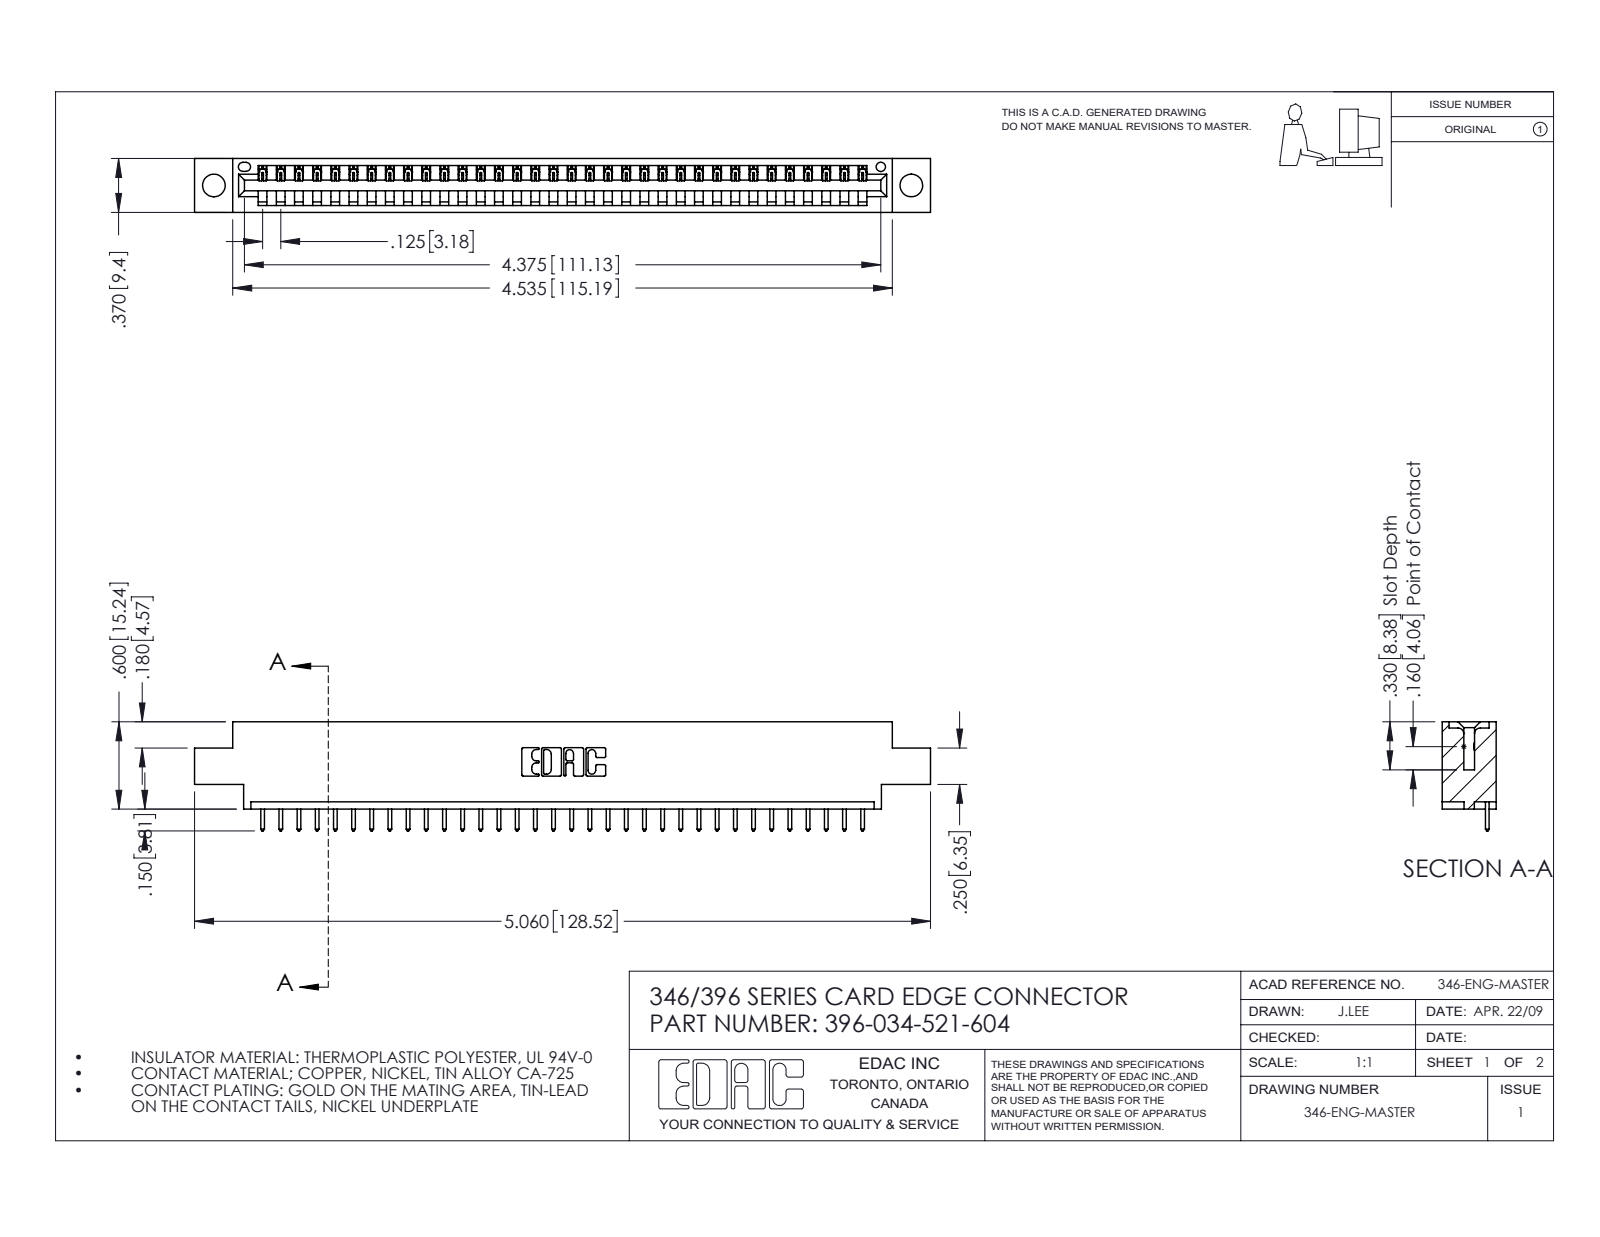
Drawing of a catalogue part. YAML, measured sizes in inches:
part_name: "396-034-521-604; 345-292-001_345-293-121; 346 Part_0.170 Offset - 0.156 Dia-TH"
step_written_by: "SolidWorks 2016 (CONFIG_CONTROL_DESIGN)"
units: inches
bodies: {solids: 35, faces: 2098, planar: 1440, cylindrical: 658, other: 0}
overall_size: [5.06, 0.75, 0.37]
volume: 0.727
surface_area: 22.29
round_holes:
  - {diameter: 0.156, count: 2}
  - {diameter: 0.064, count: 1}
partial_cylinders:
  - {radius: 0.006, count: 68}
  - {radius: 0.01, count: 68}
  - {radius: 0.01, count: 22}
  - {radius: 0.007, count: 6}
  - {radius: 0.031, count: 6}
  - {radius: 0.026, count: 3}
  - {radius: 0.031, count: 2}
  - {radius: 0.04, count: 2}
face_to_face_distances: [0.048, 0.322, 0.37, 0.25, 0.072, 0.298, 0.025, 0.148, 0.222, 0.1]
hole_center_spacings: [0.246, 4.587, 4.795]
